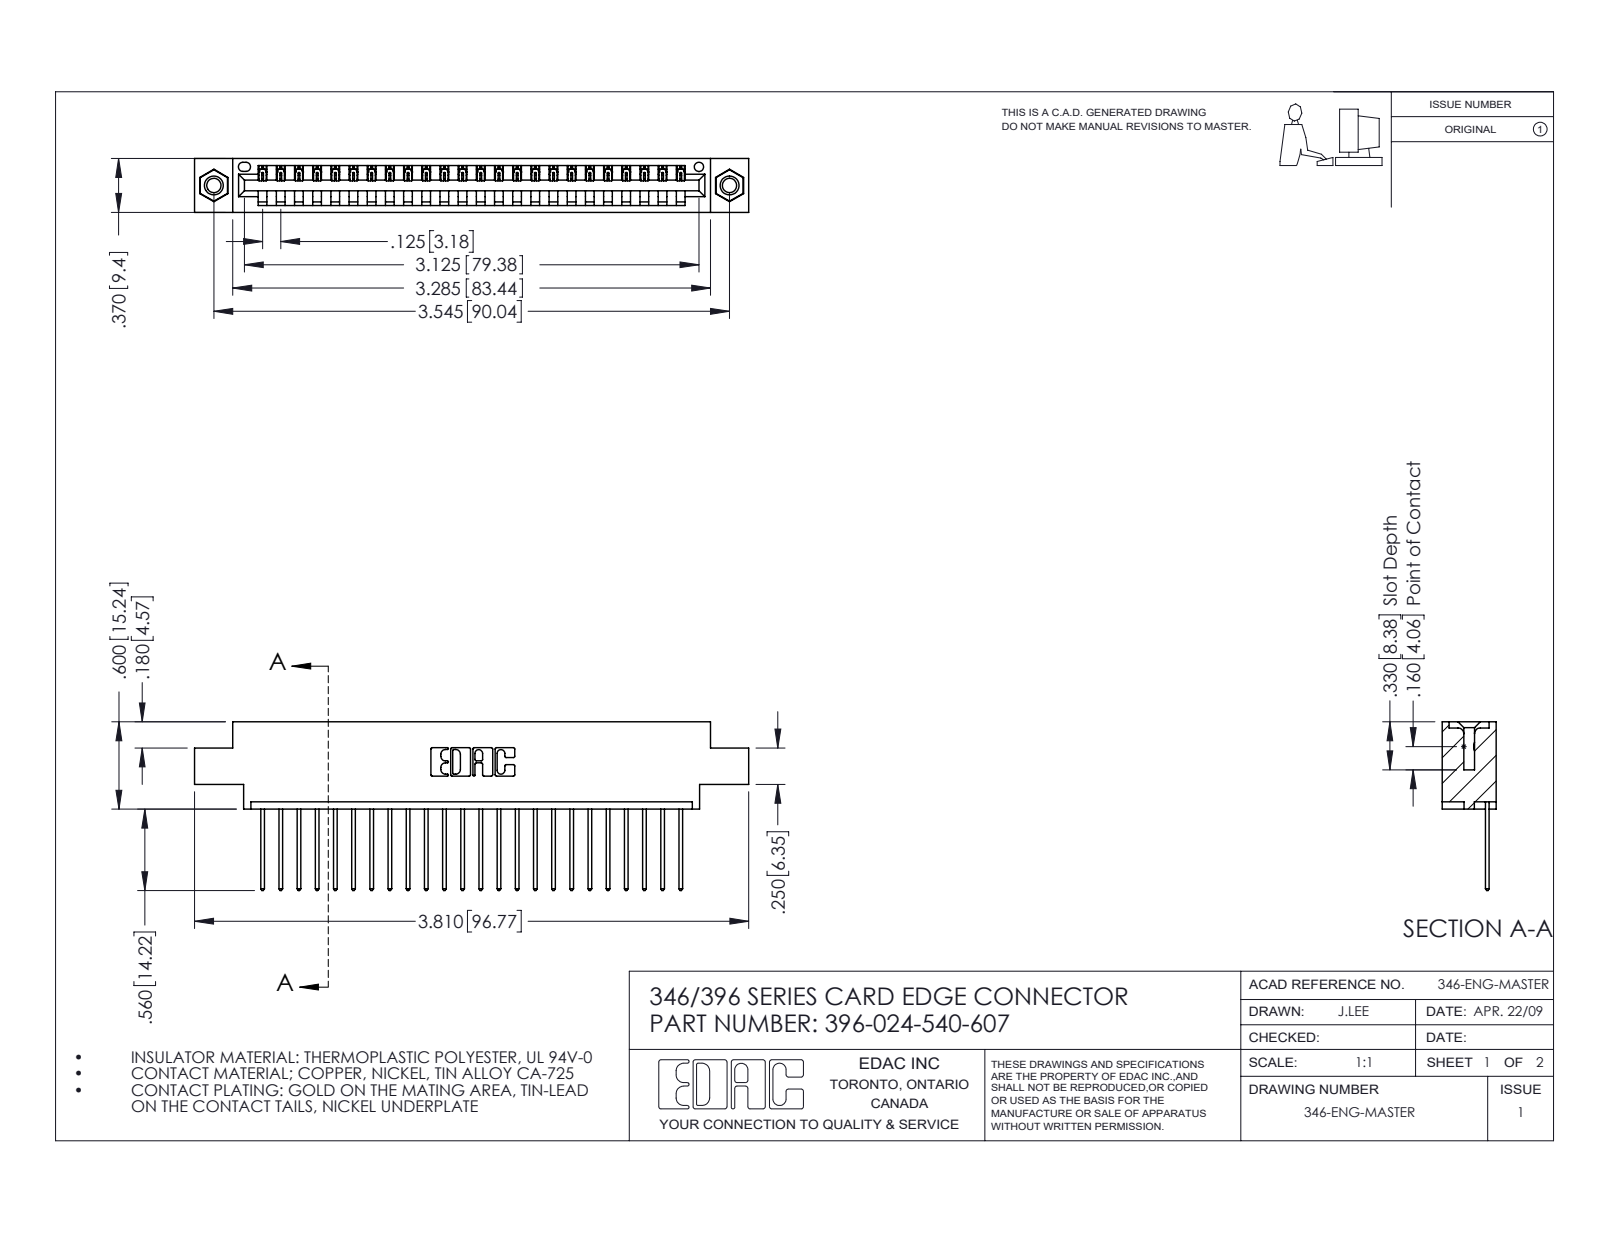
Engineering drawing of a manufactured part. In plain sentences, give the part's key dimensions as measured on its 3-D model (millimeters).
The part is named "345-250-001_345-250-005-103; 345-292-001_345-293-140; 346 Part_0.170 Offset - 0.156 Dia-TI; 396-024-540-607". Its 3-D file was written by "SolidWorks 2016 (CONFIG_CONTROL_DESIGN)". It is 27 solids with 1578 faces: 1072 planar, 490 cylindrical and 16 other. Overall it measures 96.8 by 29.5 by 9.4 millimeters. Its volume is 9 000 cubic millimeters and its surface area 11 490 square millimeters. Round holes: 2 of diameter 2.5, 2 of diameter 3.2, 2 of diameter 4, 1 of diameter 1.6. Round bosses or shafts: 2 of diameter 3.9. Partial cylindrical surfaces (rounded edges, fillets, slot ends): 48 of radius 0.2, 48 of radius 0.3, 22 of radius 0.3, 6 of radius 0.2, 6 of radius 0.8, 3 of radius 0.7, 2 of radius 0.8, 2 of radius 1. The main face-to-face distances are 1.2, 8.2, 9.4, 6.4, 1.8, 7.6, 0.6, 5.6, 3.8, 2.5. The hole center spacings are 6.2, 84.8, 90.
